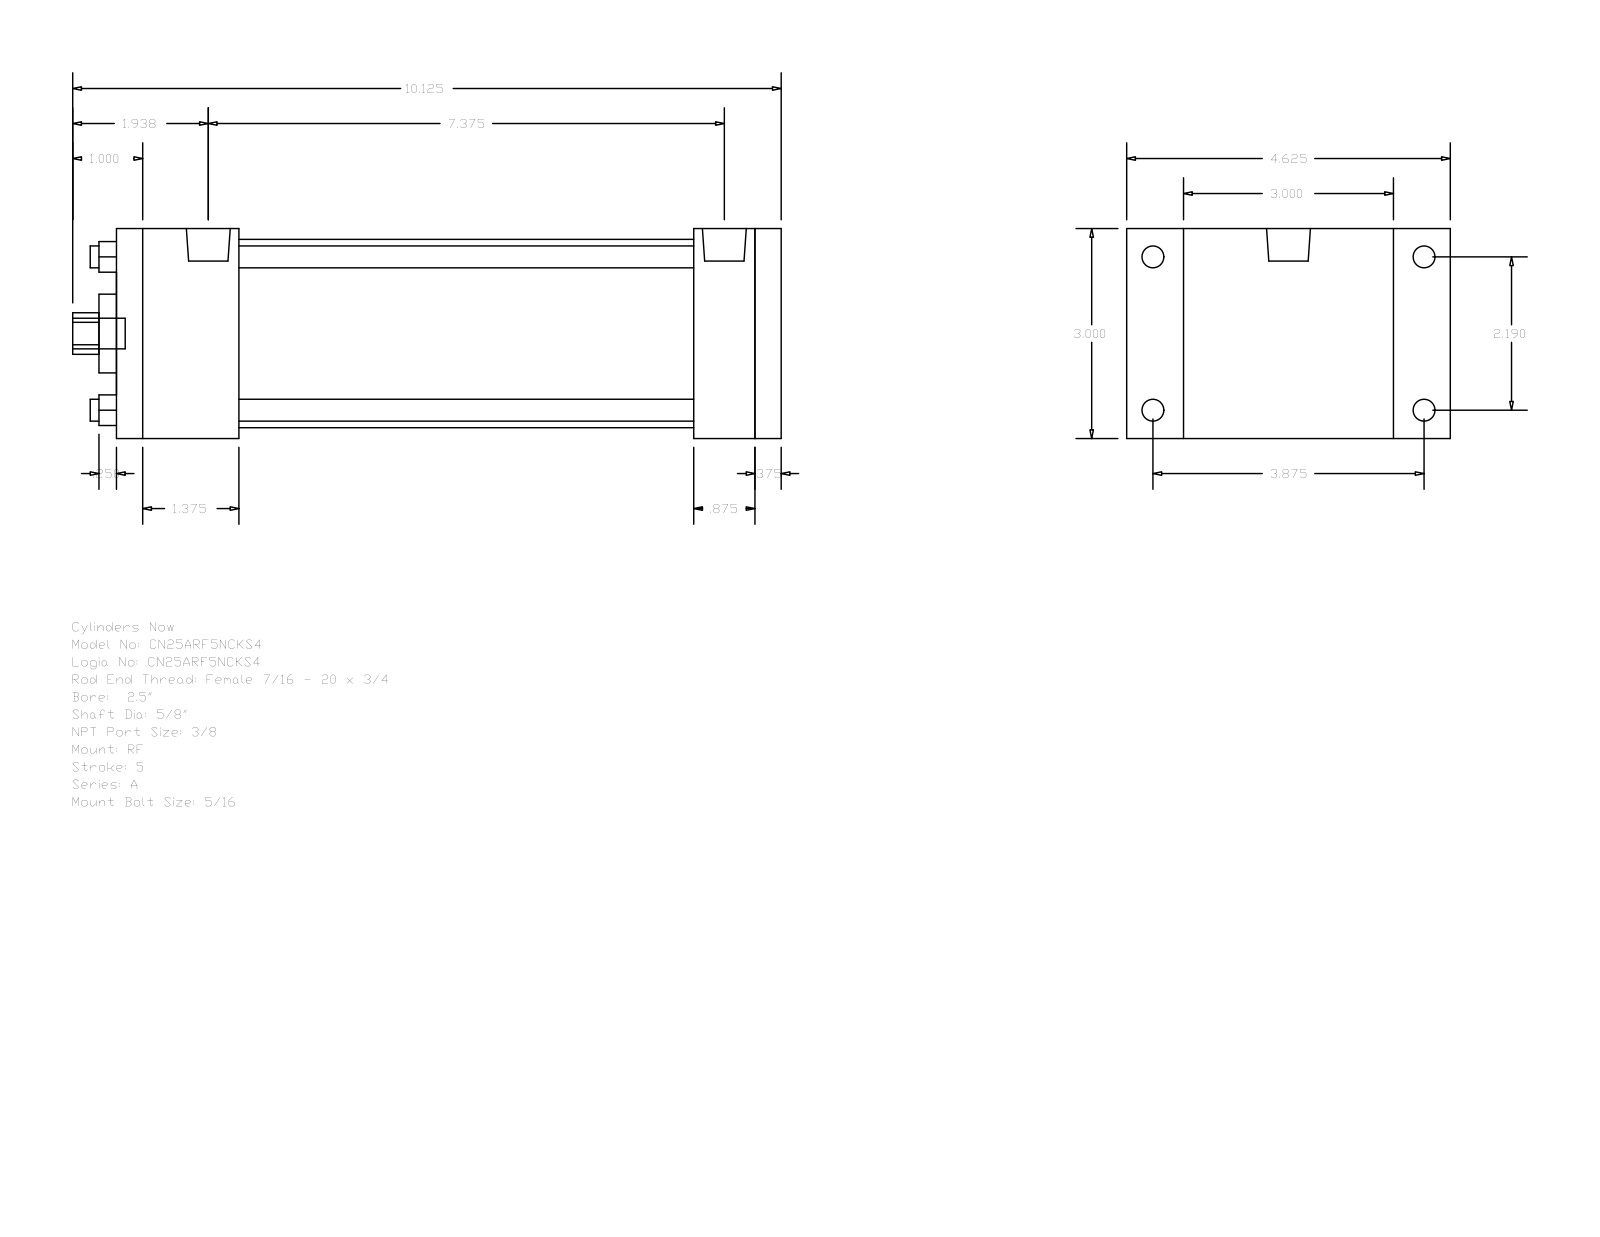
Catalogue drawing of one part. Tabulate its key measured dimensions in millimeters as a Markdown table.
| quantity | value |
| --- | --- |
| part name | A_RF__0250_0.625 |
| STEP written by | GSSL Pune (CONFIG_CONTROL_DESIGN) |
| units | millimeters |
| bodies | 0 solids, 92 faces (64 planar, 28 cylindrical, 0 other) |
| overall size | 257.18 × 117.47 × 76.2 |
| round holes (diameter × count) | 7.94 × 4, 15.88 × 1, 28.57 × 1, 68.33 × 1 |
| round bosses / shafts (diameter × count) | 7.94 × 4, 5.56 × 4, 15.93 × 2, 11.11 × 1 |
| partial cylindrical surfaces (radius × count) | 7.54 × 1 |
| main face-to-face distances | 76.2, 241.3, 9.53, 231.77, 44.45, 31.75, 209.55, 165.1, 187.32, 196.85 |
| hole center spacings | 39.33, 55.62, 78.66 |
